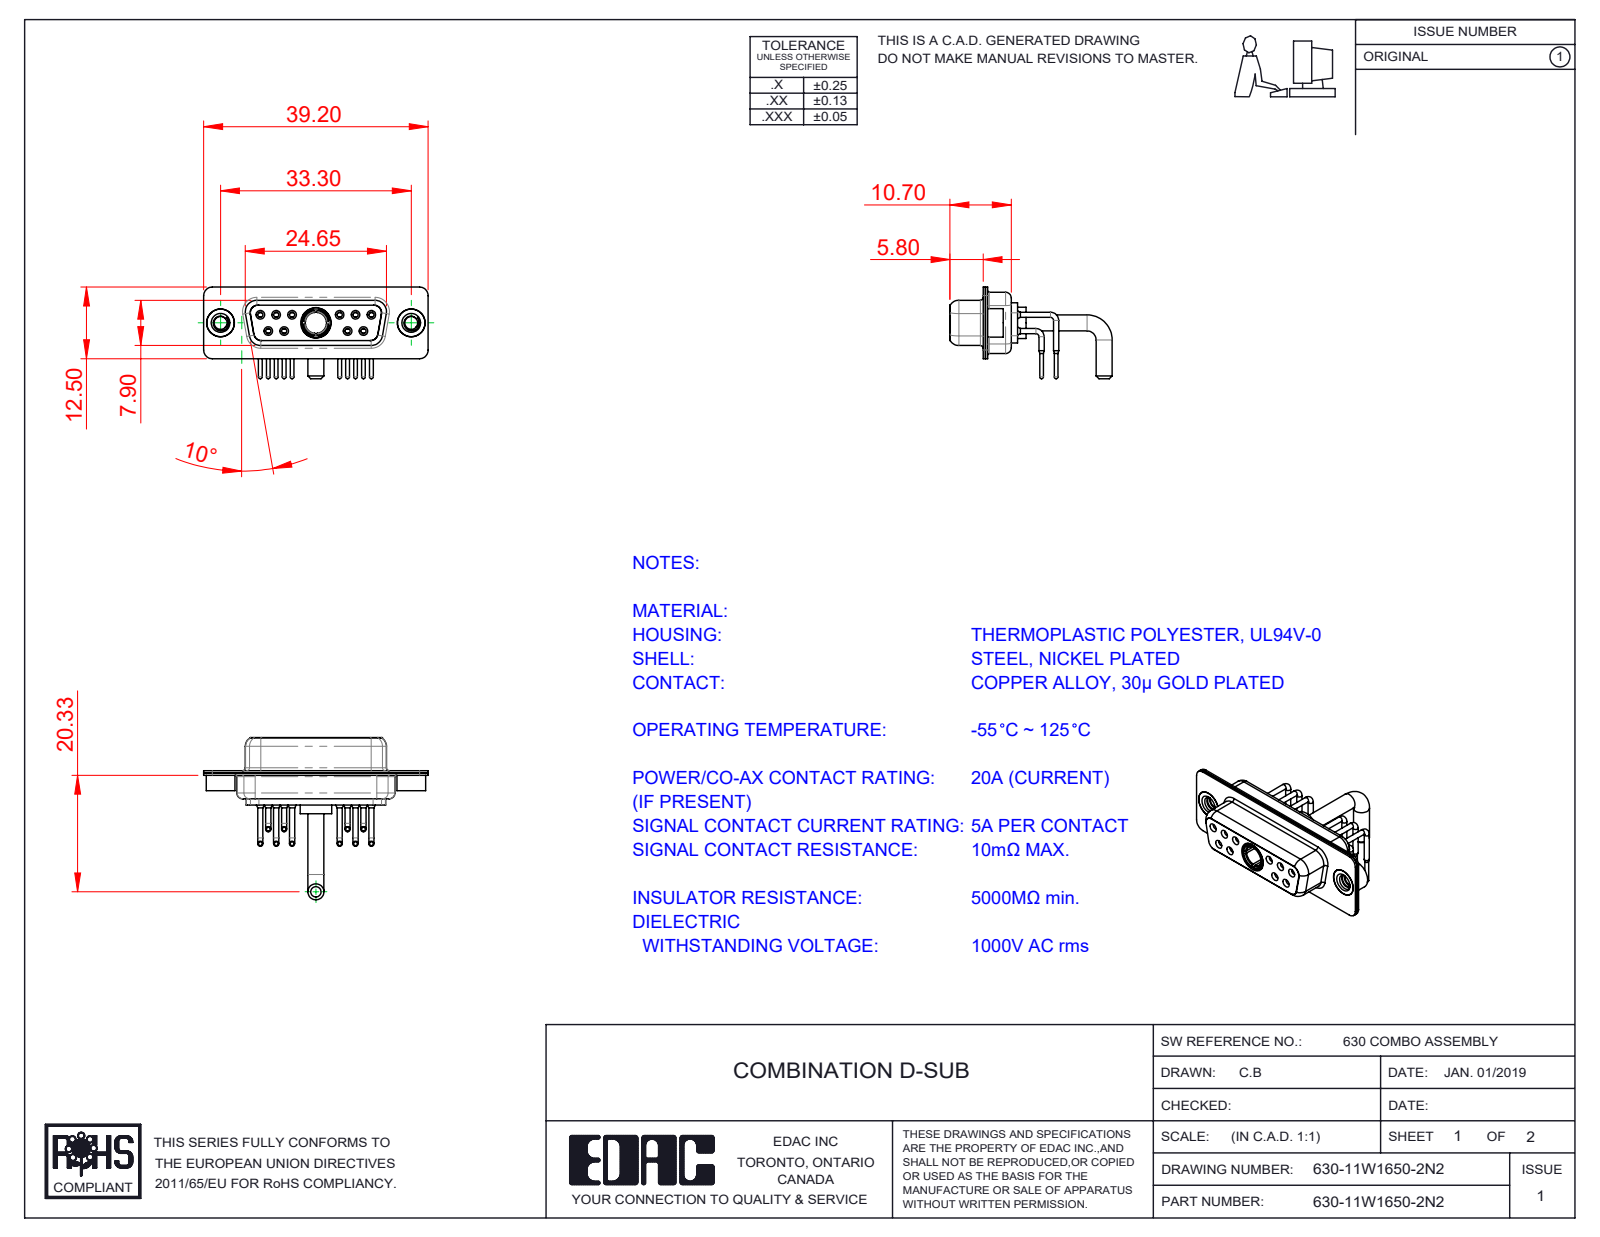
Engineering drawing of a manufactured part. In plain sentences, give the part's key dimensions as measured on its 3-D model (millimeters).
The part is named "630Combo Contact Row 2; Power Socket_Ext 20A RA; 630-11W1650-2N2; 630Combo Shell Rear_15 Contacts (+4 more)". Its 3-D file was written by "SolidWorks 2020 (CONFIG_CONTROL_DESIGN)". It is 17 solids with 887 faces: 246 planar, 392 cylindrical and 249 other. Overall it measures 39.2 by 28.33 by 16 millimeters. Its volume is 2 691 cubic millimeters and its surface area 6 335 square millimeters. Round holes: 10 of diameter 0.9, 10 of diameter 1.1, 10 of diameter 1.5, 10 of diameter 2, 6 of diameter 1.7, 4 of diameter 1.6, 3 of diameter 4.85, 2 of diameter 2.26, 2 of diameter 4, 2 of diameter 4.05, 1 of diameter 3.7, 1 of diameter 5.3. Round bosses or shafts: 10 of diameter 0.9, 10 of diameter 0.65, 6 of diameter 1.6, 2 of diameter 5, 2 of diameter 4.95, 2 of diameter 4.8, 2 of diameter 2.8, 1 of diameter 5.5. Partial cylindrical surfaces (rounded edges, fillets, slot ends): 16 of radius 1.5, 12 of radius 1.35, 12 of radius 2, 8 of radius 1.6, 4 of radius 0.25, 4 of radius 0.5, 4 of radius 0.6, 4 of radius 0.65. The main face-to-face distances are 0.4, 1.4, 0.45, 8.45, 1.8, 8.9, 0.8, 6.2, 7.05, 1.85. The hole center spacings are 3.16, 2.77, 13.85, 11.08, 16.62, 5.03, 5.04, 5.54.
